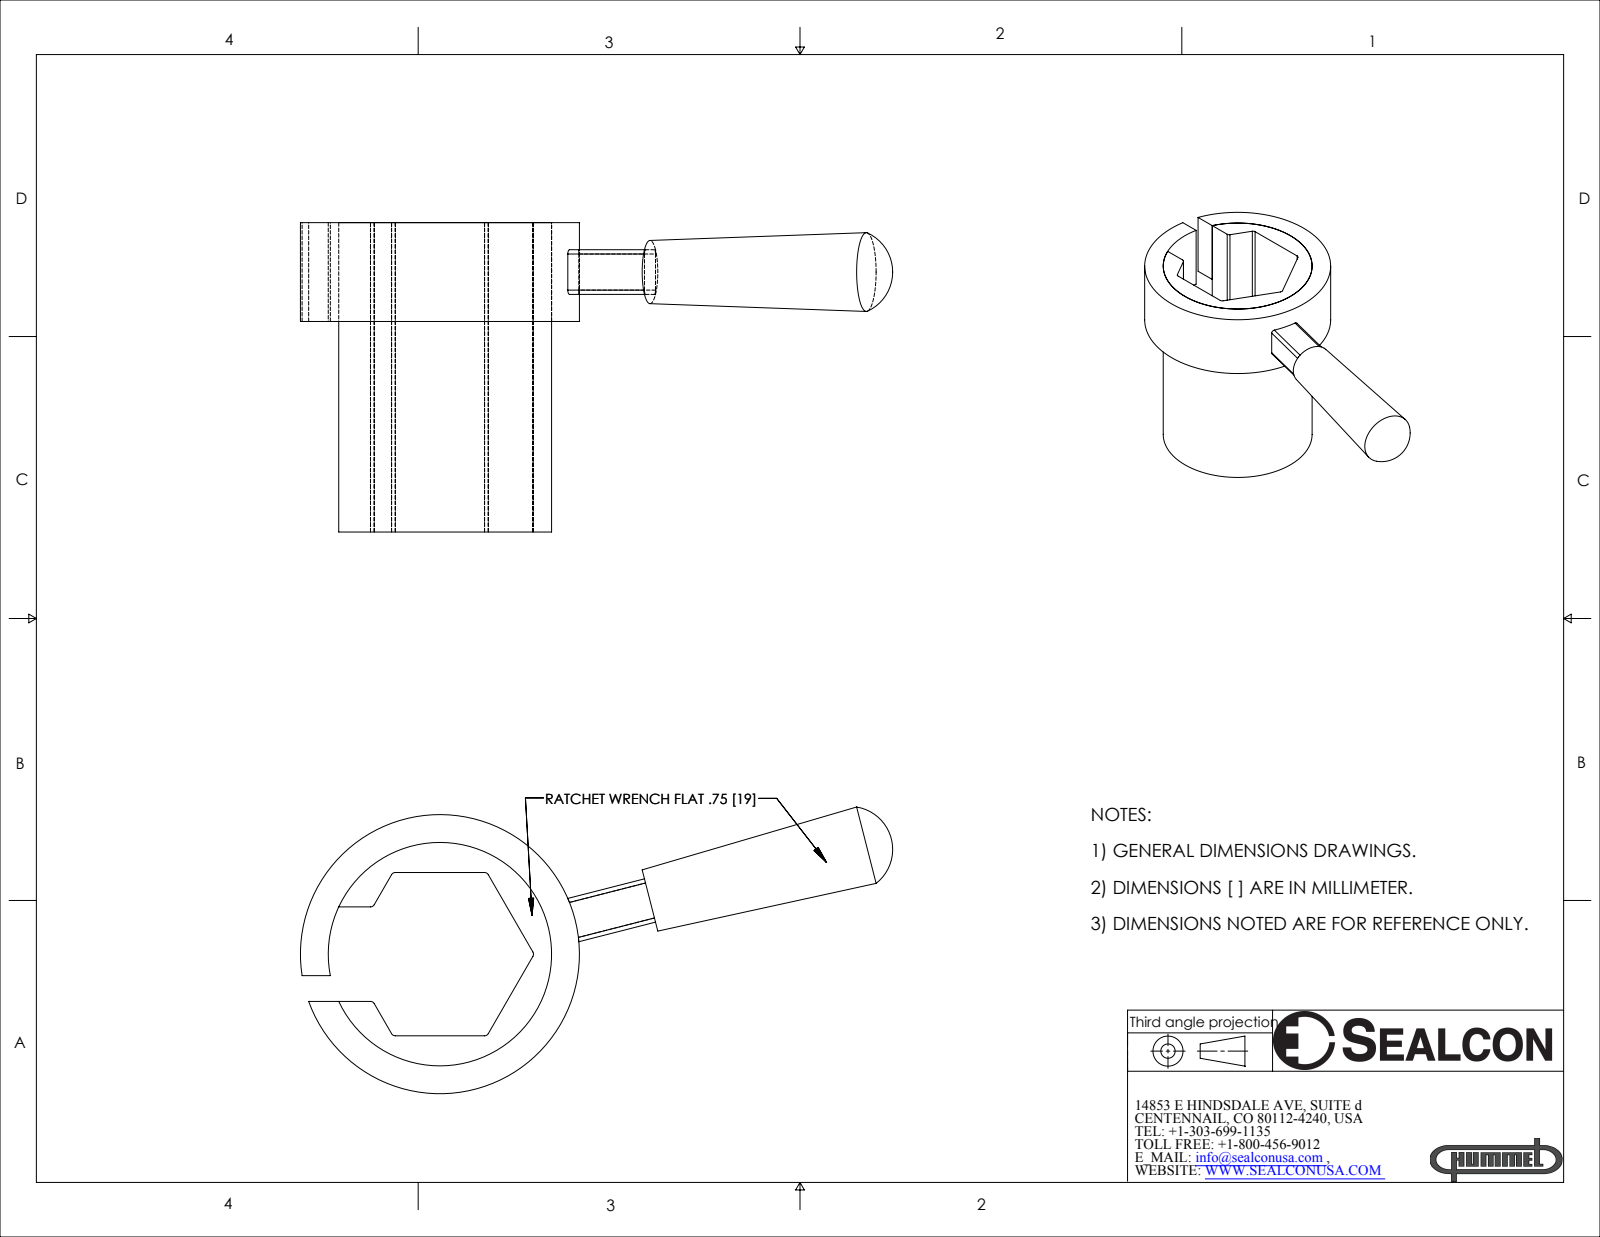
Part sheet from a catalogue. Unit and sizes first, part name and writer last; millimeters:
Units: millimetres
Overall size (bounding box): 68.95 × 36 × 33.36
Round holes (diameter × count): ⌀26 ×1
Round bosses / shafts (diameter × count): ⌀32.48 ×1
Partial cylindrical surfaces — rounded edges, fillets, slot ends (radius × count): R0.5 ×11
Main face-to-face distances: 19, 4, 15, 11.5, 24.5, 36, 11, 5.2, 3.15, 8.35
Volume: 11 647 mm³ · Surface area: 8 771 mm²
Bodies: 3 solids, 43 faces (19 planar, 20 cylindrical, 4 other)
Part name (STEP PRODUCT): R-1900-WR
STEP written by: SolidWorks 2007 (CONFIG_CONTROL_DESIGN)
